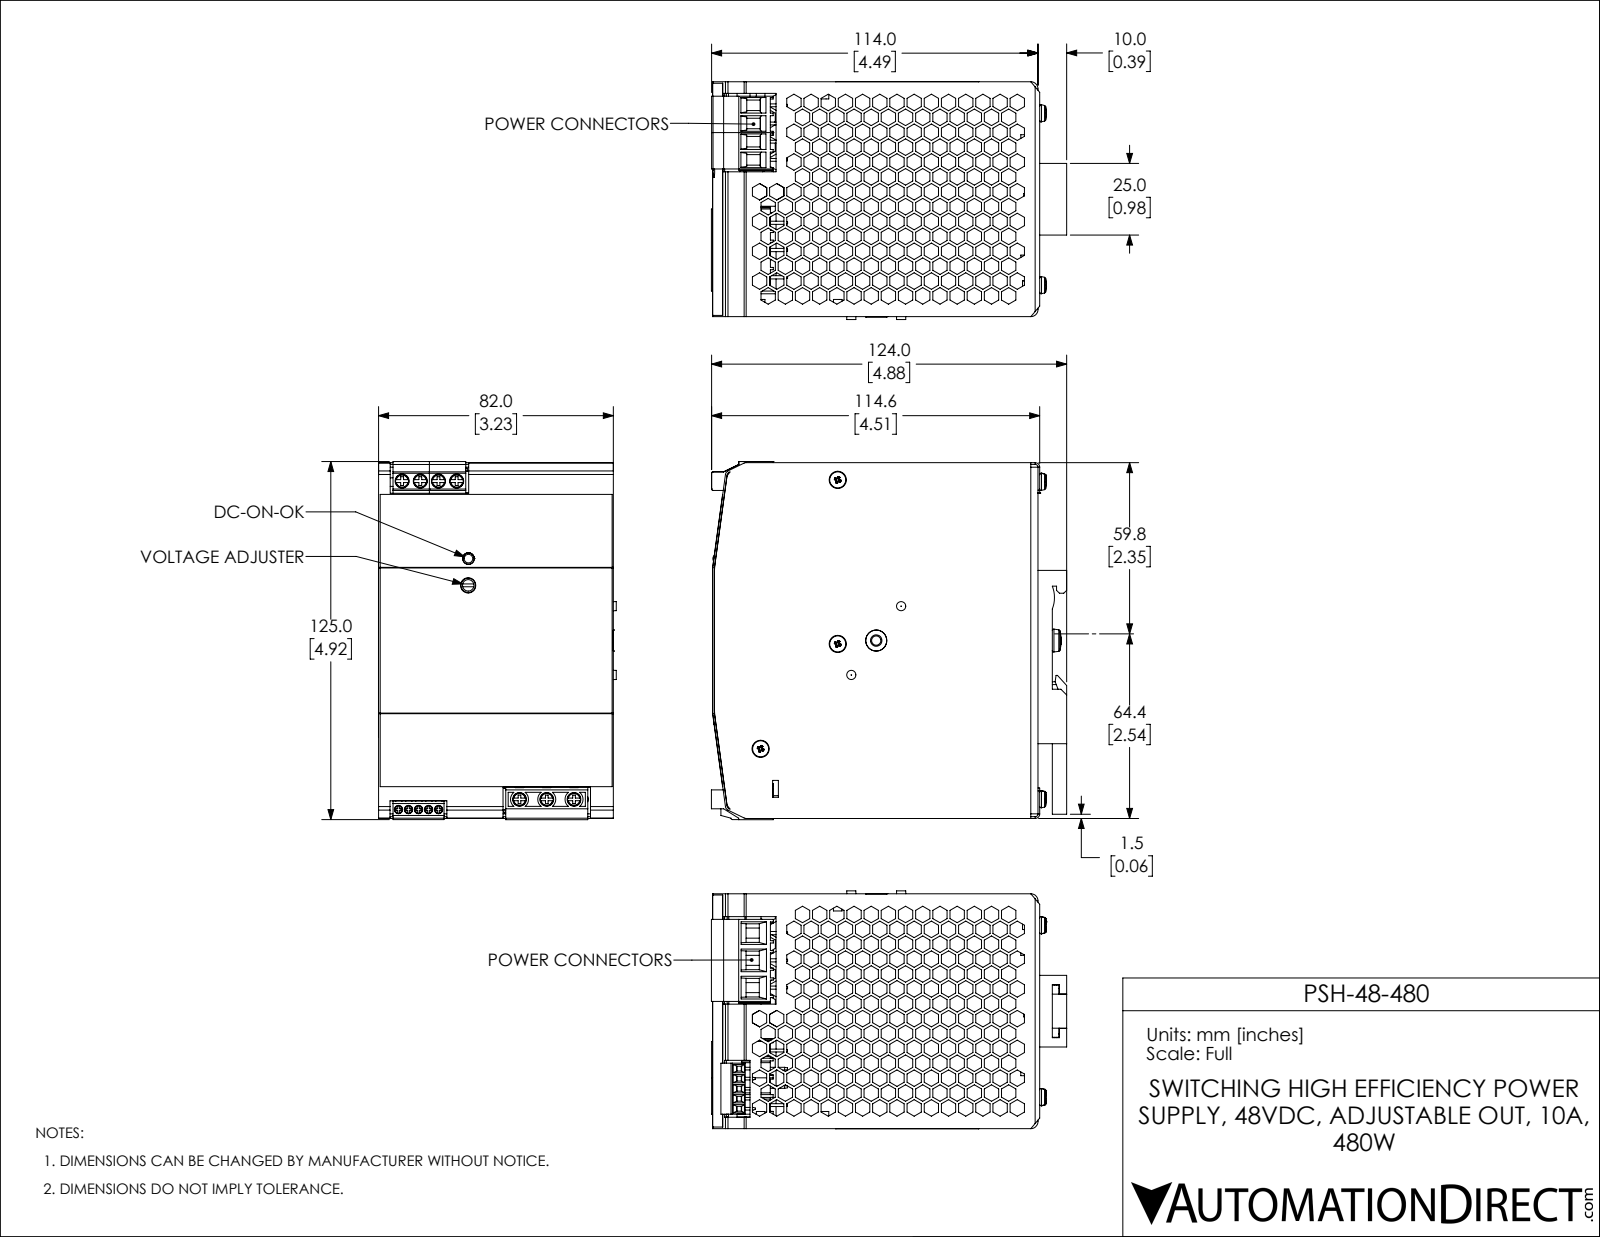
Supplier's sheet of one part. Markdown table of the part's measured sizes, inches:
| quantity | value |
| --- | --- |
| part name | PSH-X-480 |
| STEP written by | SolidWorks 2017 (AUTOMOTIVE_DESIGN) |
| units | inches |
| bodies | 21 solids, 4246 faces (3671 planar, 322 cylindrical, 253 other) |
| overall size | 4.923 × 4.884 × 3.27 |
| volume | 5.489 in³ |
| surface area | 238.3 in² |
| round holes (diameter × count) | 0.126 × 13, 0.008 × 6, 0.104 × 5, 0.114 × 5, 0.118 × 4, 0.181 × 4, 0.193 × 4, 0.193 × 4, 0.157 × 3, 0.177 × 3, 0.189 × 3, 0.118 × 1 |
| round bosses / shafts (diameter × count) | 0.118 × 19, 0.22 × 13, 0.02 × 7, 0.126 × 6, 0.11 × 5, 0.187 × 4, 0.138 × 4, 0.188 × 3 |
| partial cylindrical surfaces (radius × count) | 0.014 × 52, 0.039 × 23, 0.004 × 16, 0.063 × 13, 0.006 × 7, 0.02 × 5, 0.053 × 5, 0.124 × 5 |
| main face-to-face distances | 0.059, 3.169, 0.024, 3.228, 3.11, 4.472, 4.413, 4.866, 0.026, 4.39 |
| hole center spacings | 0.583, 0.138, 1.799, 2.09, 2.355, 2.72, 2.921, 0.25 |
